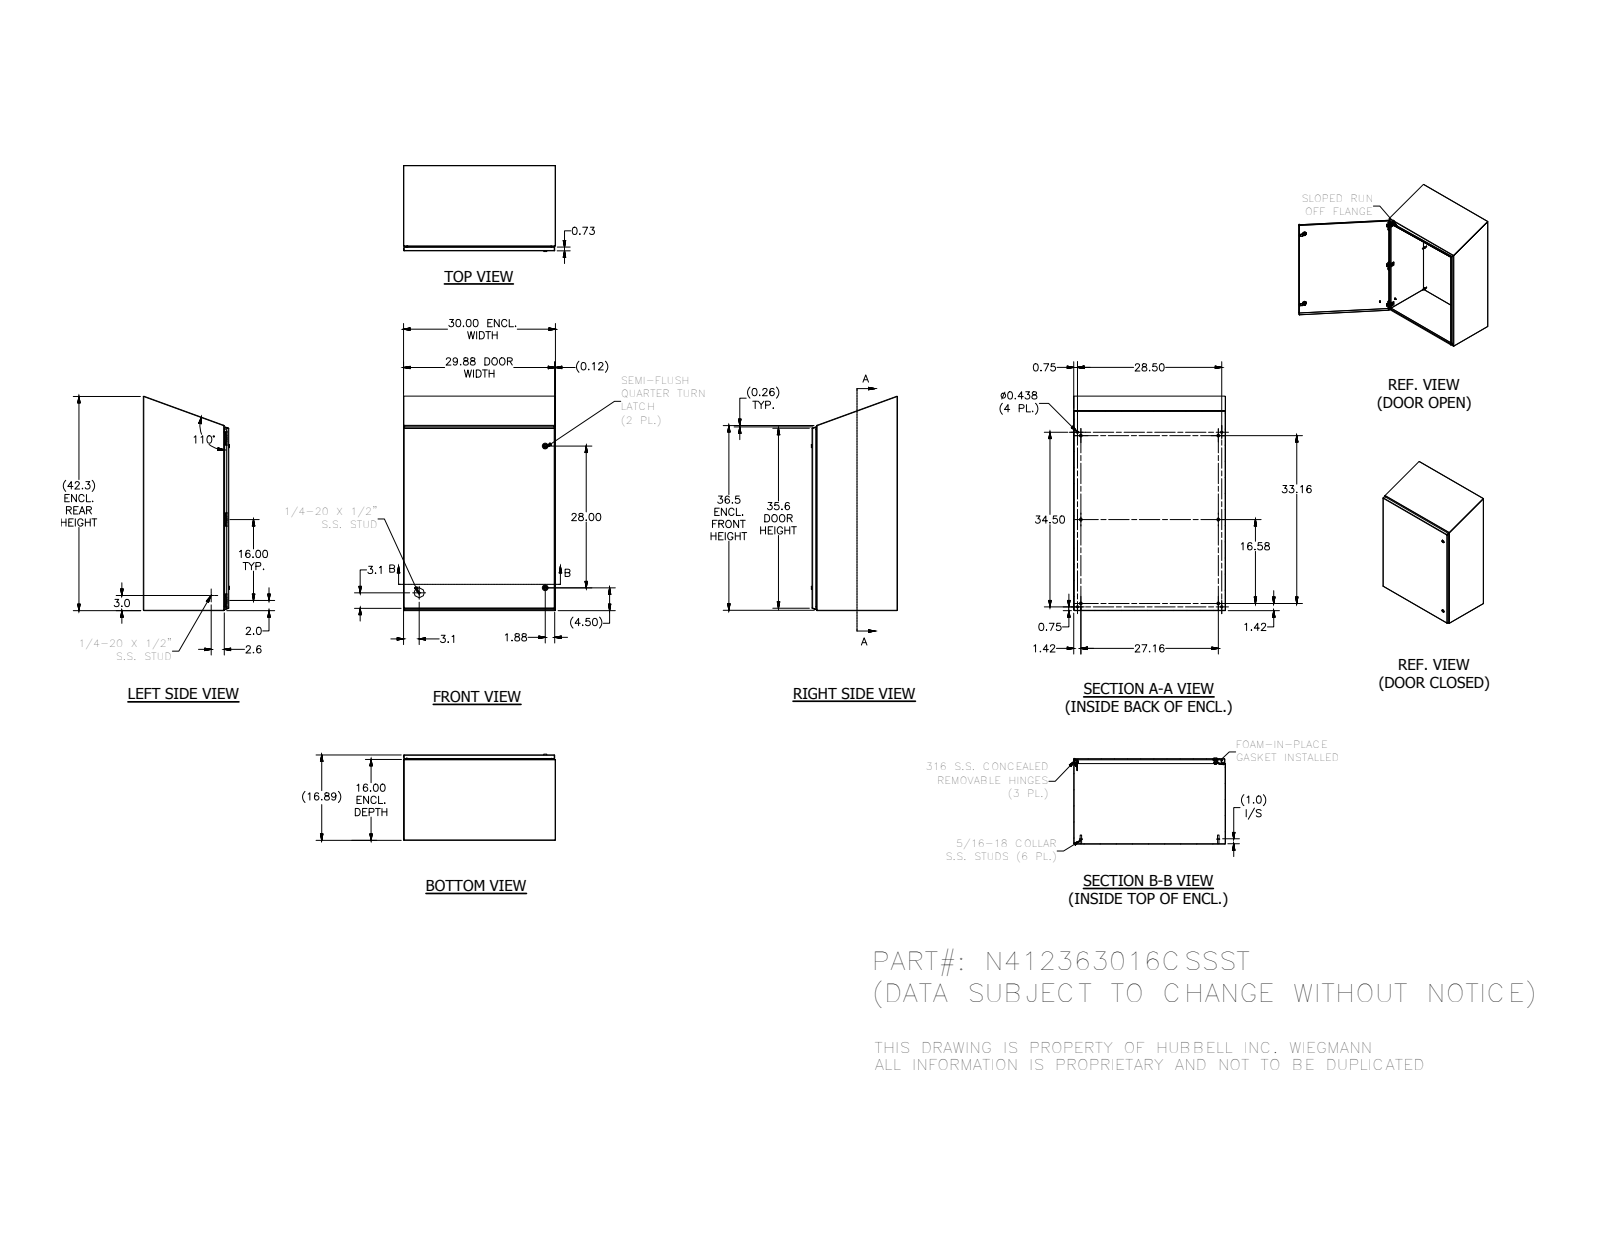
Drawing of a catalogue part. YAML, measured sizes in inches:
part_name: "N412_CSSST-assm3pcblr; N412363016CSSSTBLR; HFW3161; HFW328176 (+8 more)"
step_written_by: "Autodesk Inventor 2012 (AUTOMOTIVE_DESIGN)"
units: inches
bodies: {solids: 52, faces: 2350, planar: 906, cylindrical: 864, other: 580}
overall_size: [42.377, 30, 17.044]
volume: 360.8
surface_area: 9823
round_holes:
  - {diameter: 0.093, count: 6}
  - {diameter: 0.152, count: 6}
  - {diameter: 0.167, count: 6}
  - {diameter: 0.172, count: 6}
  - {diameter: 0.187, count: 6}
  - {diameter: 0.156, count: 4}
  - {diameter: 0.437, count: 4}
  - {diameter: 0.197, count: 2}
  - {diameter: 0.315, count: 2}
  - {diameter: 0.394, count: 2}
  - {diameter: 0.402, count: 2}
  - {diameter: 0.634, count: 2}
round_bosses_or_shafts:
  - {diameter: 0.25, count: 14}
  - {diameter: 0.563, count: 6}
  - {diameter: 0.36, count: 6}
  - {diameter: 0.32, count: 6}
  - {diameter: 0.3, count: 6}
  - {diameter: 0.275, count: 6}
  - {diameter: 0.256, count: 6}
  - {diameter: 0.164, count: 6}
partial_cylinders:
  - {radius: 0.012, count: 54}
  - {radius: 0.05, count: 38}
  - {radius: 0.031, count: 29}
  - {radius: 0.016, count: 26}
  - {radius: 0.125, count: 24}
  - {radius: 0.02, count: 23}
  - {radius: 0.105, count: 15}
  - {radius: 0.032, count: 12}
face_to_face_distances: [0.074, 16.813, 29.926, 16.739, 16.887, 29.852, 30, 15.926, 0.887, 0.813]
hole_center_spacings: [16, 32, 16.008, 0.5, 0.656, 0.66, 1.307, 1.311]
